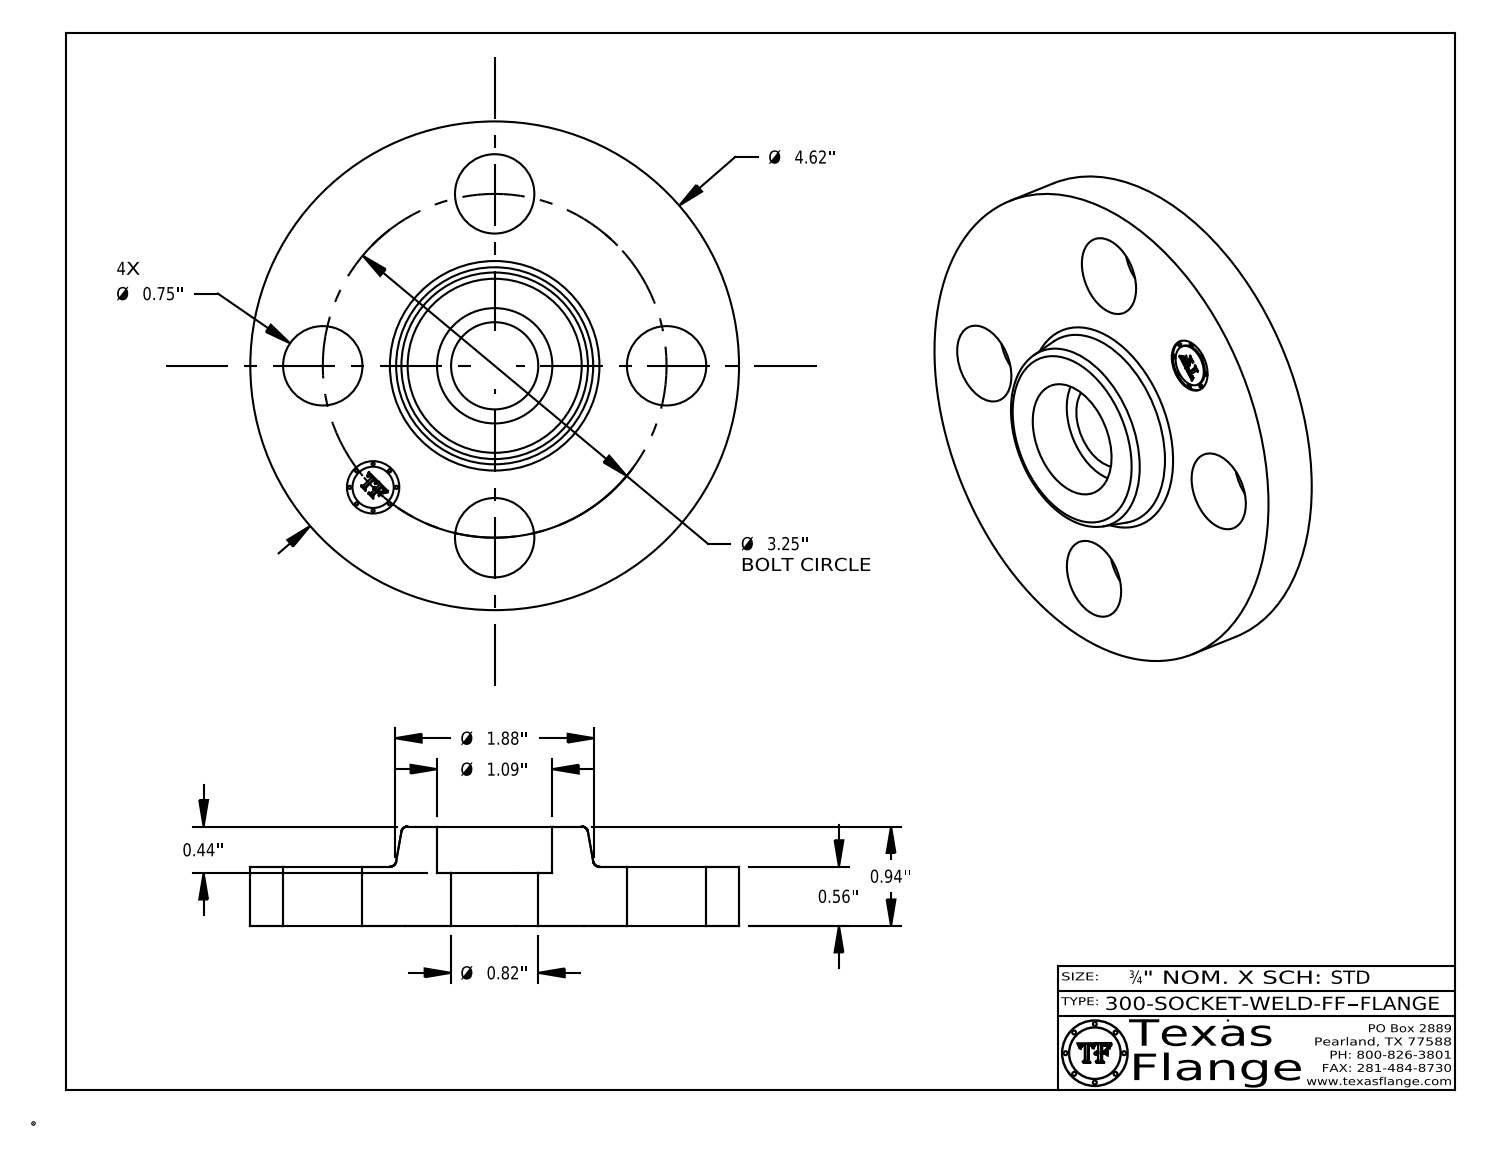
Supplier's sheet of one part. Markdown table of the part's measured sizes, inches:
| quantity | value |
| --- | --- |
| part name | 300-SOCKET-WELD-FF |
| STEP written by | CATIA V5 STEP AP214 (AUTOMOTIVE_DESIGN) |
| units | inches |
| bodies | 1 solid, 410 faces (370 planar, 34 cylindrical, 6 other) |
| overall size | 4.62 × 4.62 × 0.94 |
| volume | 8.701 in³ |
| surface area | 46.85 in² |
| round holes (diameter × count) | 0.75 × 4, 0.495 × 1, 0.824 × 1, 1.09 × 1 |
| round bosses / shafts (diameter × count) | 0.03 × 8, 4.62 × 1, 0.39 × 1 |
| main face-to-face distances | 0.56, 0.94, 0.38, 0.5, 0.06, 0.44, 0.545, 0.045, 0.015, 0.395 |
| hole center spacings | 1.625, 2.298, 1.244, 3.003, 3.25 |
